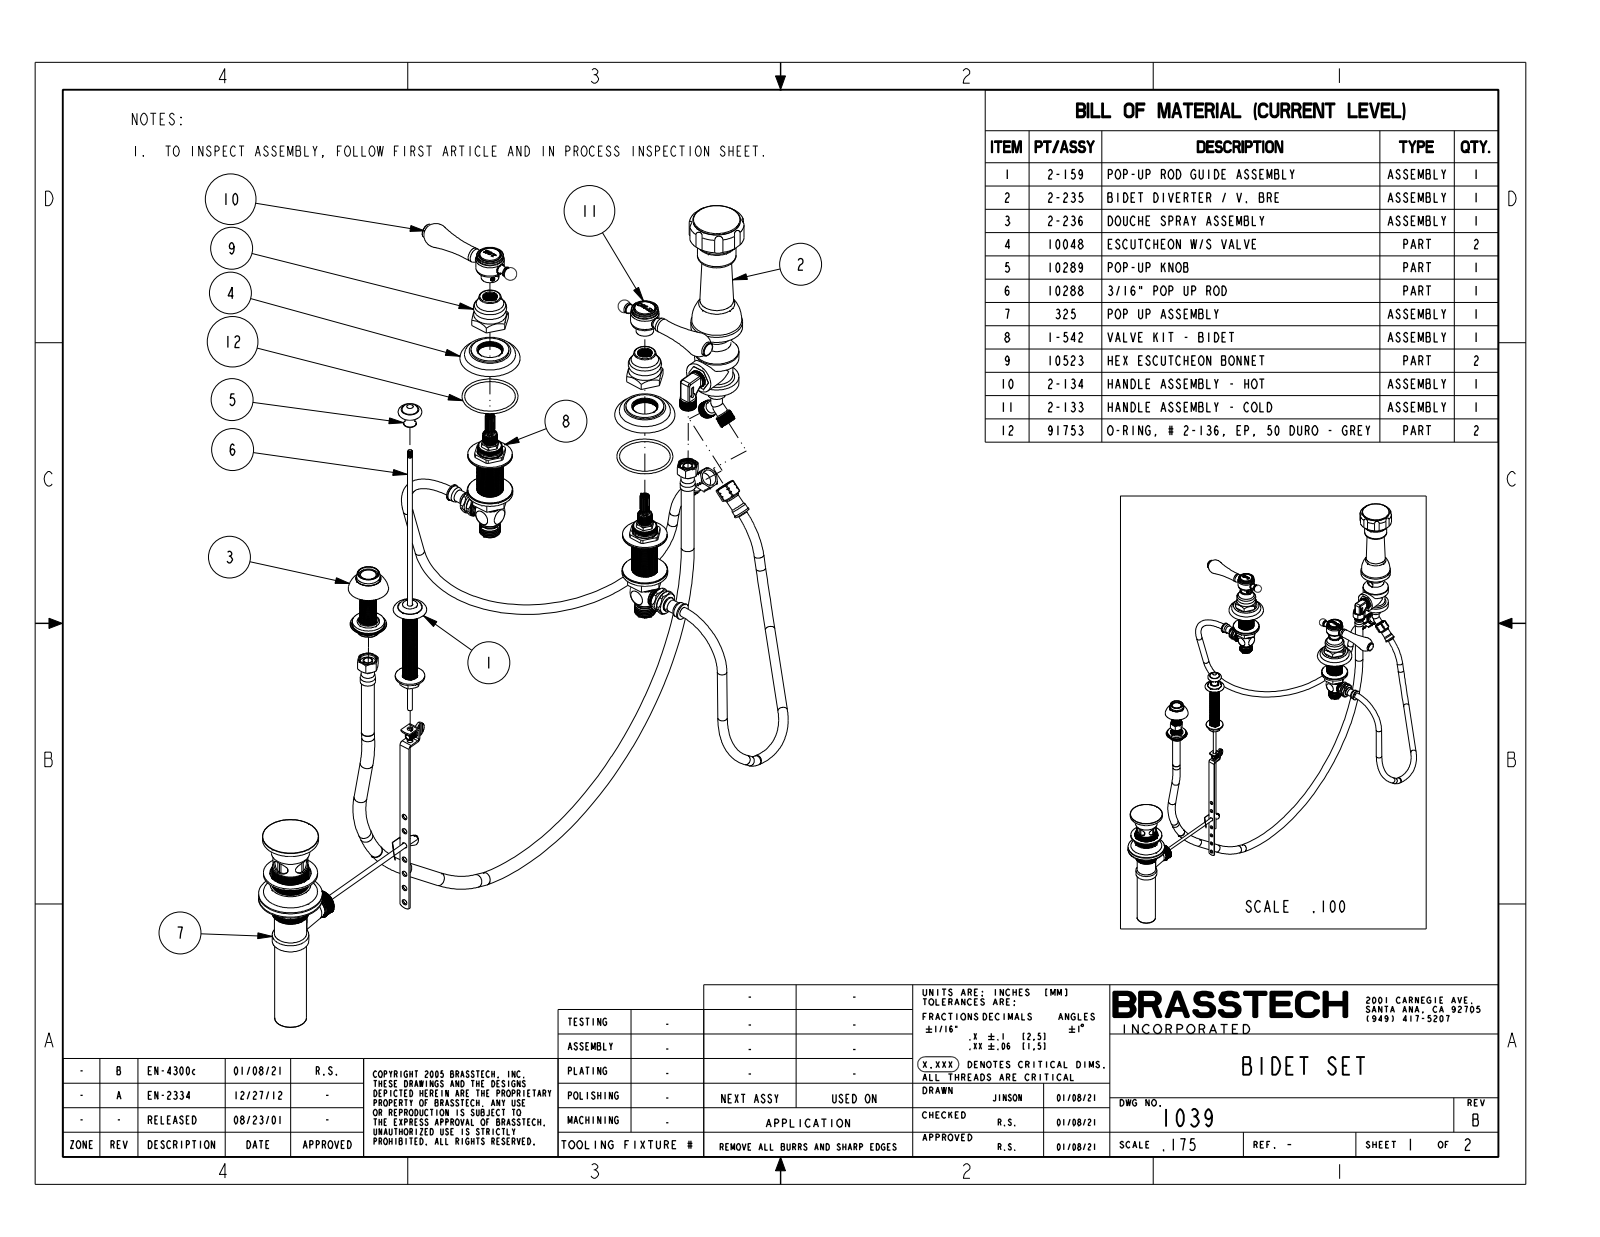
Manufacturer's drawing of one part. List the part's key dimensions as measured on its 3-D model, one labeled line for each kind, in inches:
Part name (STEP PRODUCT): 1039
STEP written by: CREO PARAMETRIC BY PTC INC, 2018400 (CONFIG_CONTROL_DESIGN)
Units: inches
Bodies: 5 solids, 469 faces (161 planar, 126 cylindrical, 182 other)
Overall size (bounding box): 22.855 × 14.745 × 5.353
Volume: 21.8 in³ · Surface area: 101.4 in²
Round holes (diameter × count): ⌀0.855 ×2, ⌀0.41 ×1, ⌀0.625 ×1, ⌀0.792 ×1, ⌀0.94 ×1
Round bosses / shafts (diameter × count): ⌀1.482 ×2, ⌀1.115 ×2, ⌀1.055 ×2, ⌀0.687 ×2, ⌀2.025 ×1, ⌀1.52 ×1, ⌀0.925 ×1, ⌀0.775 ×1
Partial cylindrical surfaces — rounded edges, fillets, slot ends (radius × count): R0.21 ×8, R0.006 ×7, R0.024 ×7, R0.03 ×5, R0.048 ×3, R0.018 ×2, R0.036 ×2, R0.041 ×2
Main face-to-face distances: 6.928, 1.313, 0.375, 3.468, 3.093, 1.313, 8.241, 5.615, 0.437, 0.062
Hole centre spacings: 12.649, 8
